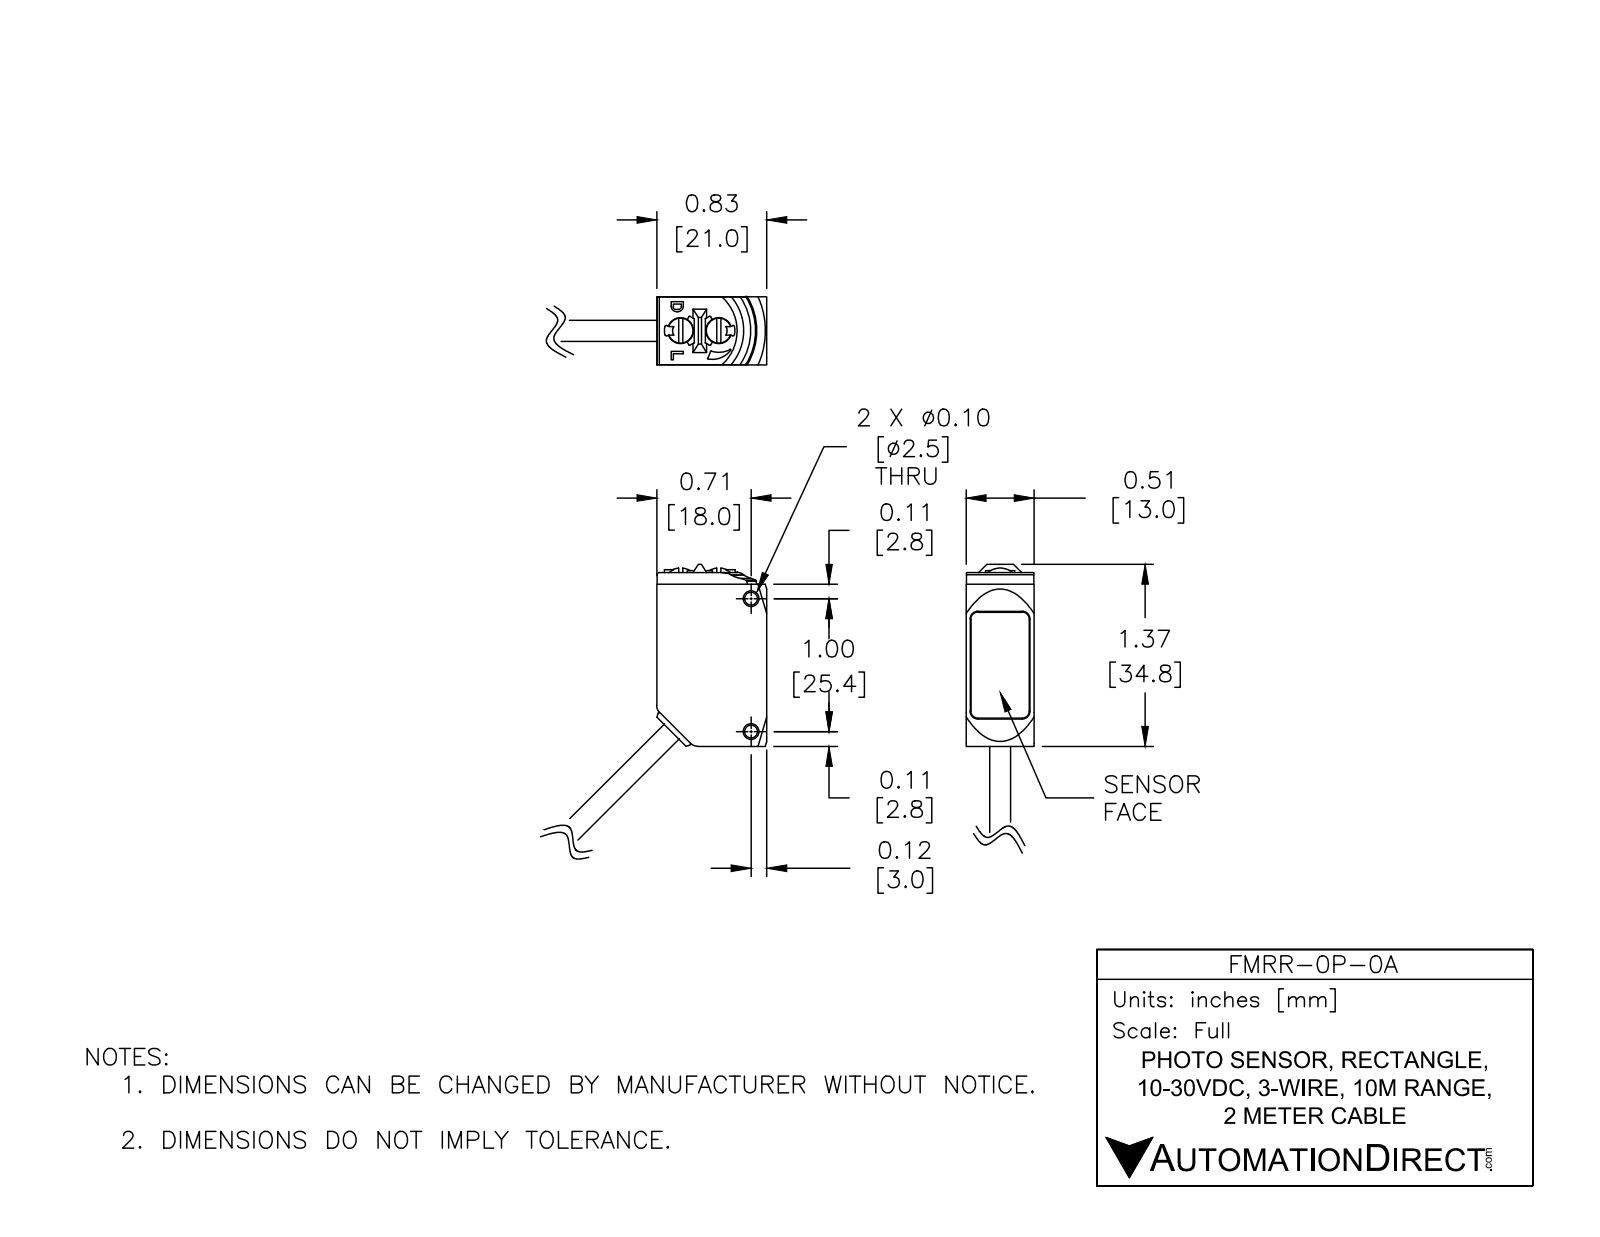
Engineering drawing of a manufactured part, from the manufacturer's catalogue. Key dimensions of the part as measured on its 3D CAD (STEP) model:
Part name (STEP PRODUCT): FMRR-0P-0A
STEP written by: SolidWorks 2017 (AUTOMOTIVE_DESIGN)
Units: inches
Bodies: 1 solid, 186 faces (89 planar, 72 cylindrical, 25 other)
Overall size (bounding box): 2.084 × 1.541 × 0.512
Volume: 0.542 in³ · Surface area: 5.476 in²
Round holes (diameter × count): ⌀0.097 ×2, ⌀0.197 ×2
Round bosses / shafts (diameter × count): ⌀0.189 ×2, ⌀0.157 ×1
Partial cylindrical surfaces — rounded edges, fillets, slot ends (radius × count): R0.018 ×7, R0.02 ×7, R0.008 ×4, R0.01 ×4, R0.051 ×4, R0.059 ×4, R0.004 ×3, R0.018 ×2
Main face-to-face distances: 0.512, 0.827, 1.307, 0.035, 0.51, 0.031, 0.48, 0.037, 0.474, 0.472
Hole centre spacings: 0.287, 1
